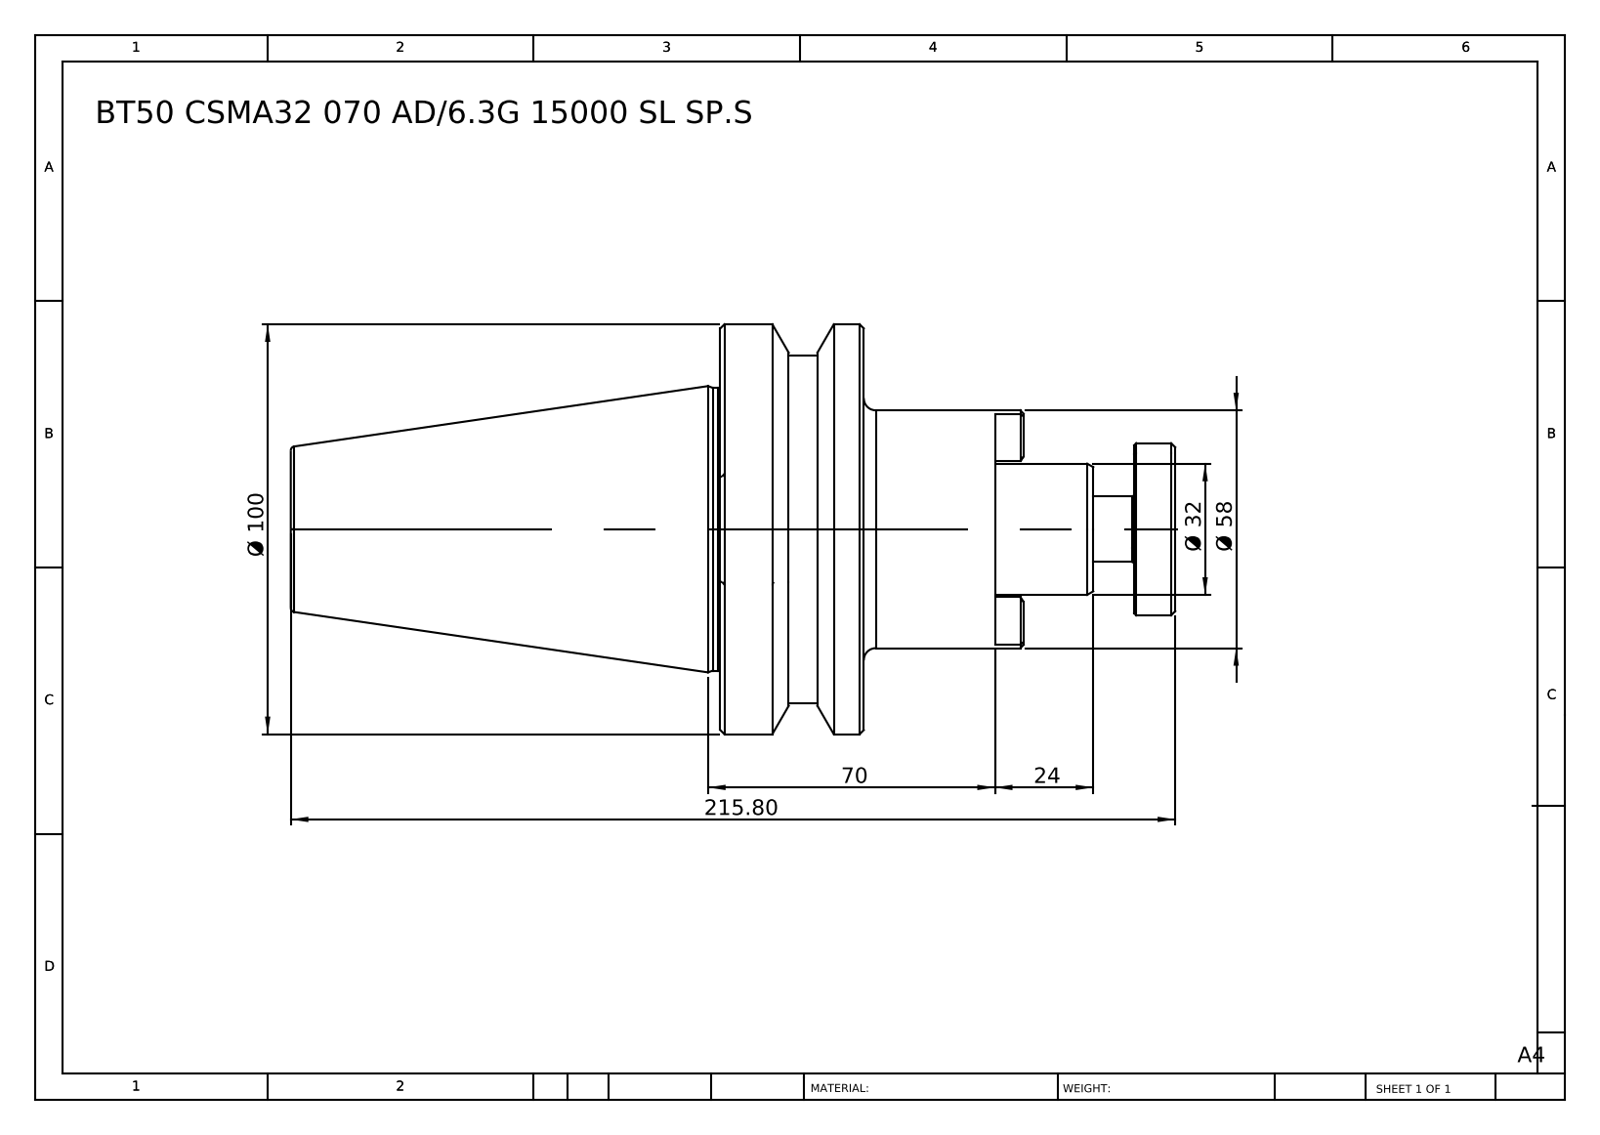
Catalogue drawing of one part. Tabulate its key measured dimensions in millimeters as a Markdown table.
| quantity | value |
| --- | --- |
| part name | BT50 CSMA32 070 AD-6.3G 15000 SL SP.S |
| STEP written by | SolidWorks 2014 (CONFIG_CONTROL_DESIGN) |
| units | millimeters |
| bodies | 1 solid, 76 faces (20 planar, 18 cylindrical, 38 other) |
| overall size | 215.8 × 100 × 100 |
| volume | 632 155 mm³ |
| surface area | 57 063 mm² |
| round bosses / shafts (diameter × count) | 100 × 1, 85 × 1, 69 × 1, 58 × 1, 42 × 1, 32 × 1, 16 × 1 |
| partial cylindrical surfaces (radius × count) | 18 × 1 |
| main face-to-face distances | 35, 10, 32, 67, 44, 76, 111, 215.8, 171.8, 139.8 |
